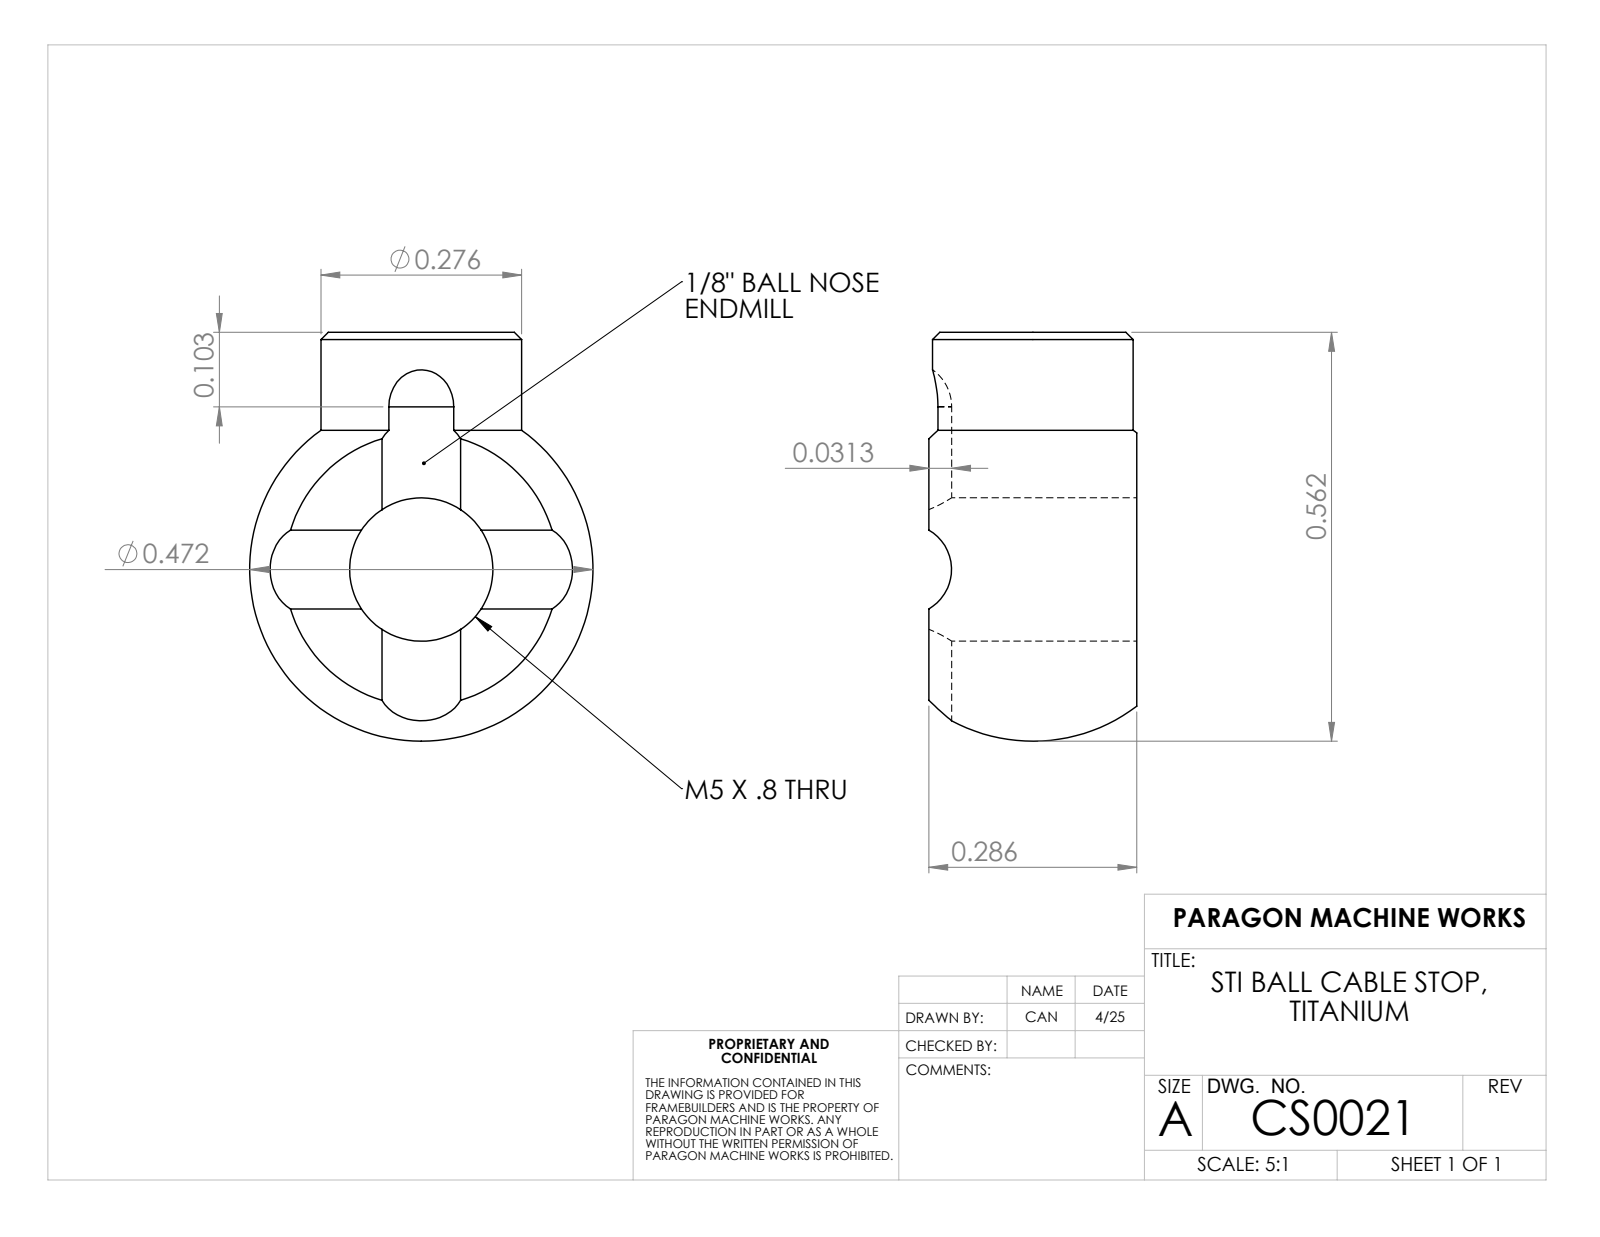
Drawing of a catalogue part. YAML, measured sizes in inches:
part_name: "CS0021"
step_written_by: "SolidWorks 2023 (AUTOMOTIVE_DESIGN)"
units: inches
bodies: {solids: 1, faces: 19, planar: 6, cylindrical: 8, other: 5}
overall_size: [0.562, 0.472, 0.286]
volume: 0.041
surface_area: 0.863
round_holes:
  - {diameter: 0.197, count: 1}
round_bosses_or_shafts:
  - {diameter: 0.276, count: 1}
partial_cylinders:
  - {radius: 0.062, count: 1}
  - {radius: 0.063, count: 1}
face_to_face_distances: [0.286]
